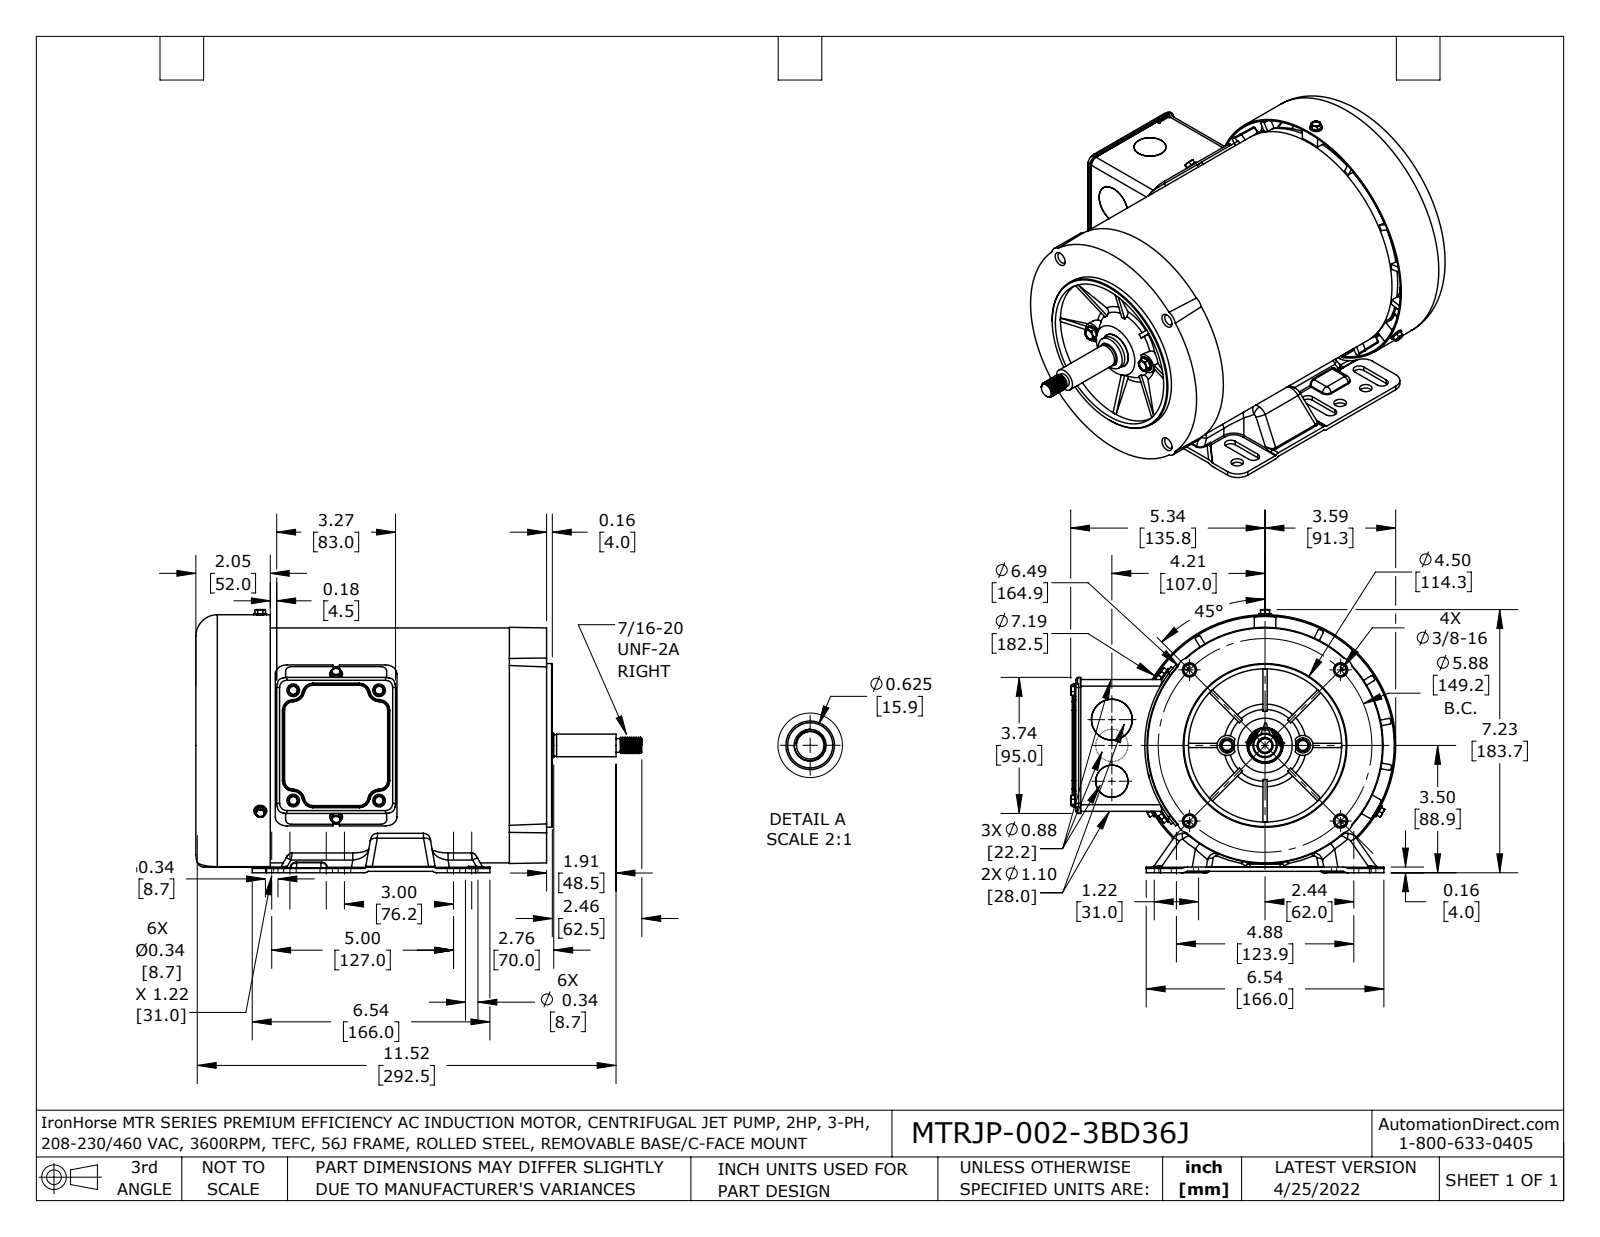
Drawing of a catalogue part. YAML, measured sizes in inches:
part_name: "MTRJP-002-3BD36J redcmb1 coord fxt"
step_written_by: "SolidWorks 2021 (AUTOMOTIVE_DESIGN)"
units: inches
bodies: {solids: 29, faces: 2729, planar: 658, cylindrical: 899, other: 1172}
overall_size: [12.264, 8.938, 7.234]
volume: 46.27
surface_area: 892.8
round_holes:
  - {diameter: 0.197, count: 10}
  - {diameter: 0.219, count: 9}
  - {diameter: 0.276, count: 8}
  - {diameter: 0.136, count: 7}
  - {diameter: 0.217, count: 6}
  - {diameter: 0.328, count: 6}
  - {diameter: 0.344, count: 6}
  - {diameter: 0.15, count: 4}
  - {diameter: 0.177, count: 4}
  - {diameter: 0.313, count: 4}
  - {diameter: 0.134, count: 2}
  - {diameter: 0.273, count: 2}
round_bosses_or_shafts:
  - {diameter: 0.164, count: 9}
  - {diameter: 0.348, count: 8}
  - {diameter: 0.236, count: 6}
  - {diameter: 0.414, count: 2}
  - {diameter: 0.19, count: 2}
  - {diameter: 7.185, count: 1}
  - {diameter: 4.5, count: 1}
  - {diameter: 0.945, count: 1}
partial_cylinders:
  - {radius: 0.118, count: 109}
  - {radius: 0.039, count: 65}
  - {radius: 0.157, count: 32}
  - {radius: 0.02, count: 30}
  - {radius: 0.138, count: 26}
  - {radius: 0.079, count: 18}
  - {radius: 0.276, count: 18}
  - {radius: 0.172, count: 12}
face_to_face_distances: [0.039, 0.118, 0.063, 0.157, 9.646, 9.606, 0.079, 3.559, 3.087, 0.047]
hole_center_spacings: [4.221, 3.031, 0.094, 2.32, 2.409, 2.937, 2.979, 3.748]
